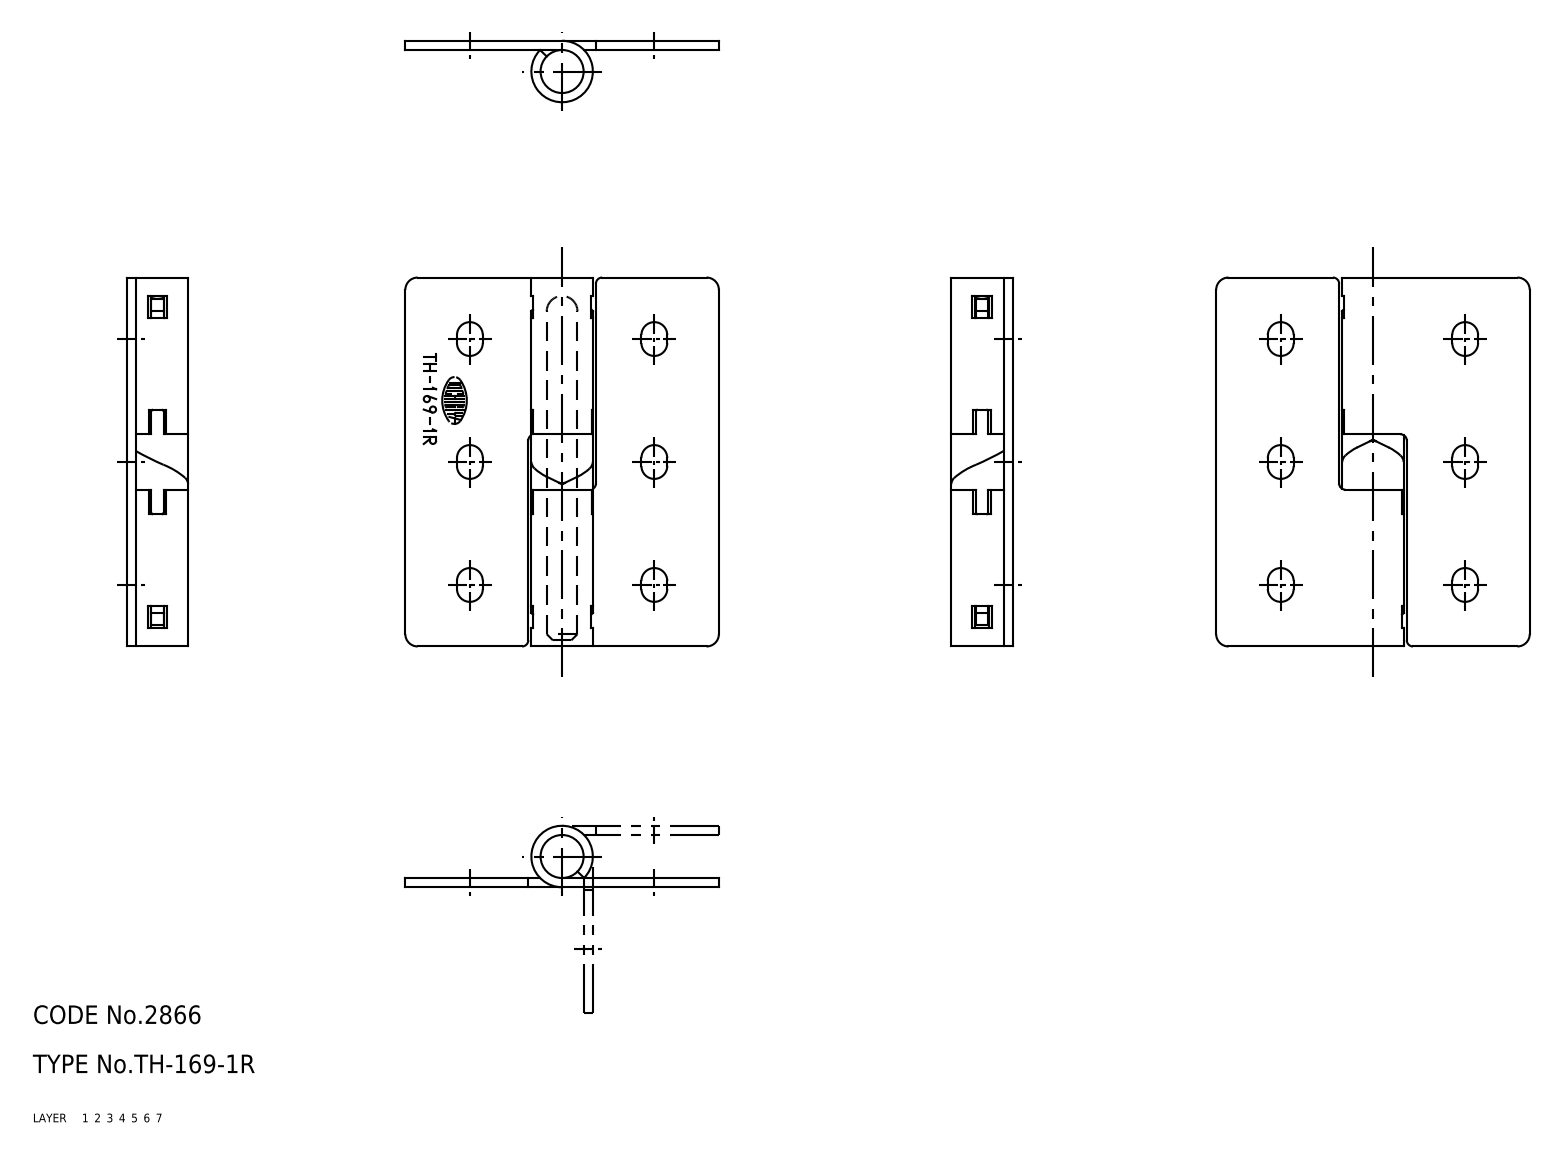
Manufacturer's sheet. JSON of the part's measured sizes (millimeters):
{"part_name": "67119481; 67119494", "step_written_by": "CADfix (AUTOMOTIVE_DESIGN)", "units": "millimeters", "bodies": {"solids": 2, "faces": 198, "planar": 0, "cylindrical": 0, "other": 198}, "overall_size": [60, 51, 10], "volume_mm3": 8178, "surface_area_mm2": 9161}
